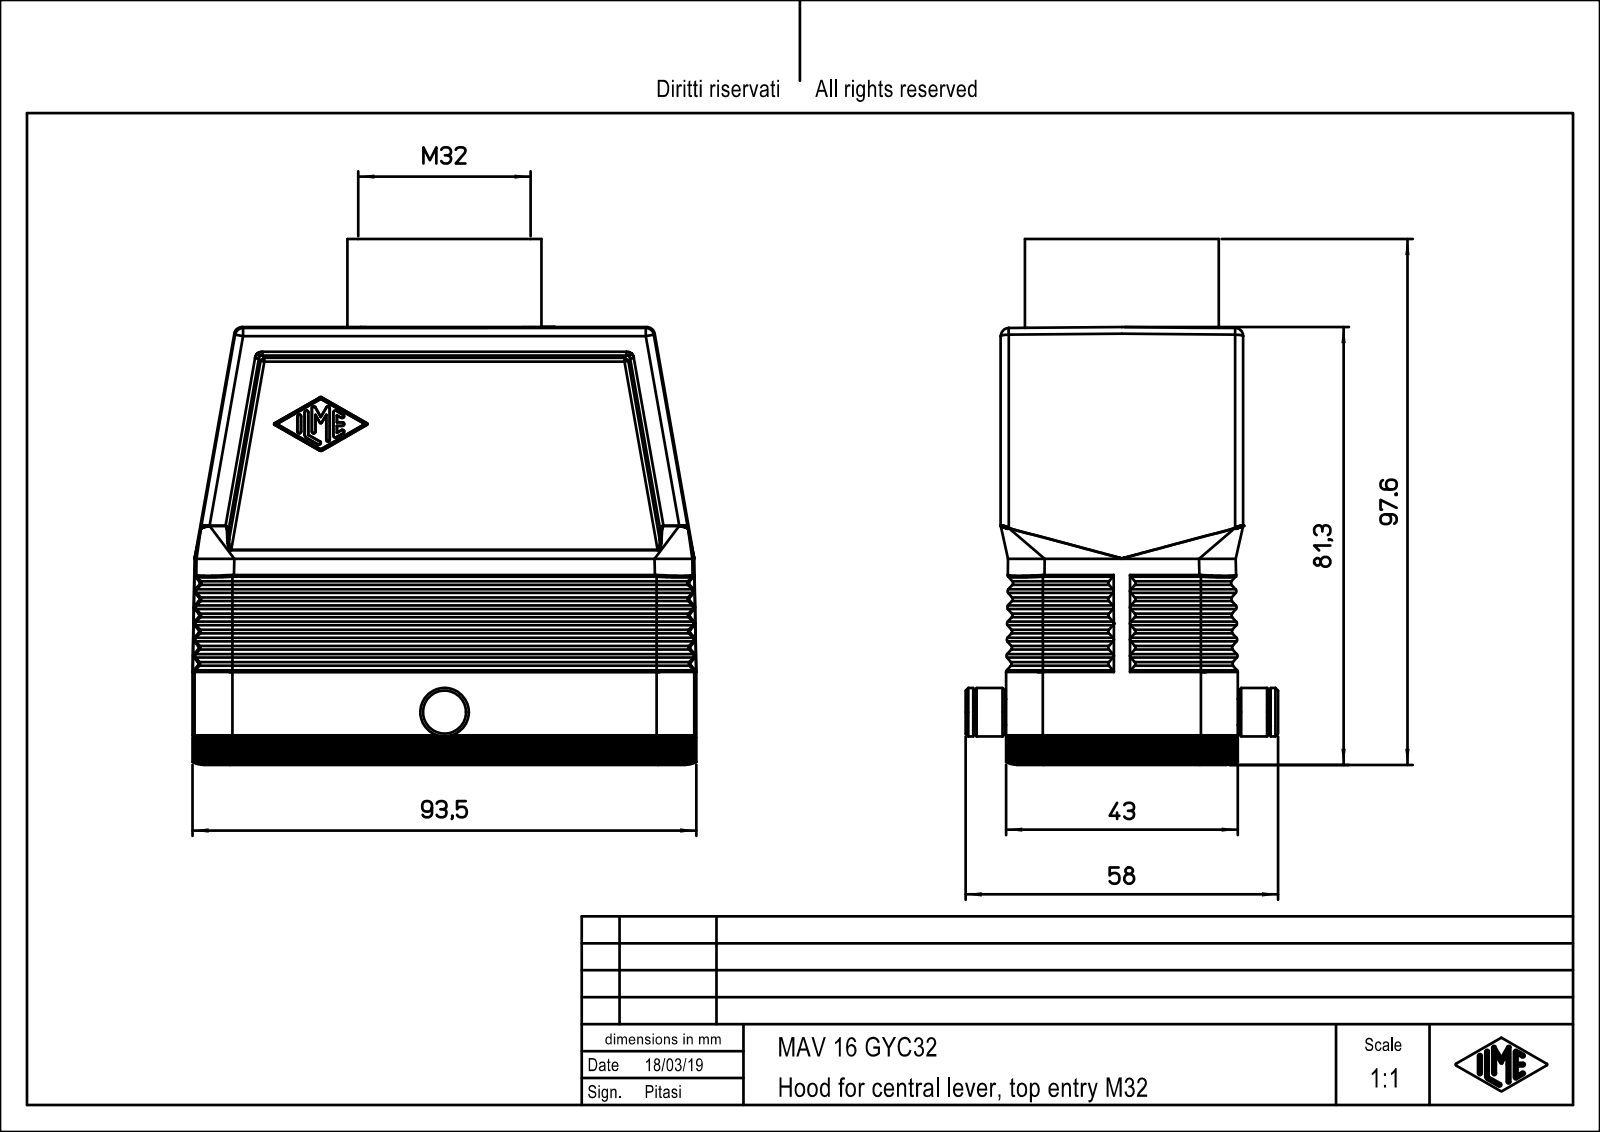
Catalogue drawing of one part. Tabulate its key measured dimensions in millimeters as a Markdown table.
| quantity | value |
| --- | --- |
| part name | MAV_16_GYC32 |
| STEP written by | PTC Creo Elements/Direct Modeling 19.0E 27-Jun-2016 (C) Parametric Technology GmbH (AUTOMOTIVE_DESIGN) |
| units | millimeters |
| bodies | 1 solid, 595 faces (229 planar, 184 cylindrical, 182 other) |
| overall size | 97.25 × 93.5 × 58 |
| volume | 108 707 mm³ |
| surface area | 51 731 mm² |
| round holes (diameter × count) | 27 × 1 |
| round bosses / shafts (diameter × count) | 36 × 1, 32 × 1, 9 × 1, 4.8 × 1 |
| partial cylindrical surfaces (radius × count) | 0.5 × 84, 1 × 16, 7 × 12, 1.5 × 10, 3 × 8, 3.5 × 4, 4 × 4, 4.2 × 4 |
| main face-to-face distances | 43, 1, 2, 4, 6.01, 7, 44, 39, 4.01, 8.01 |
